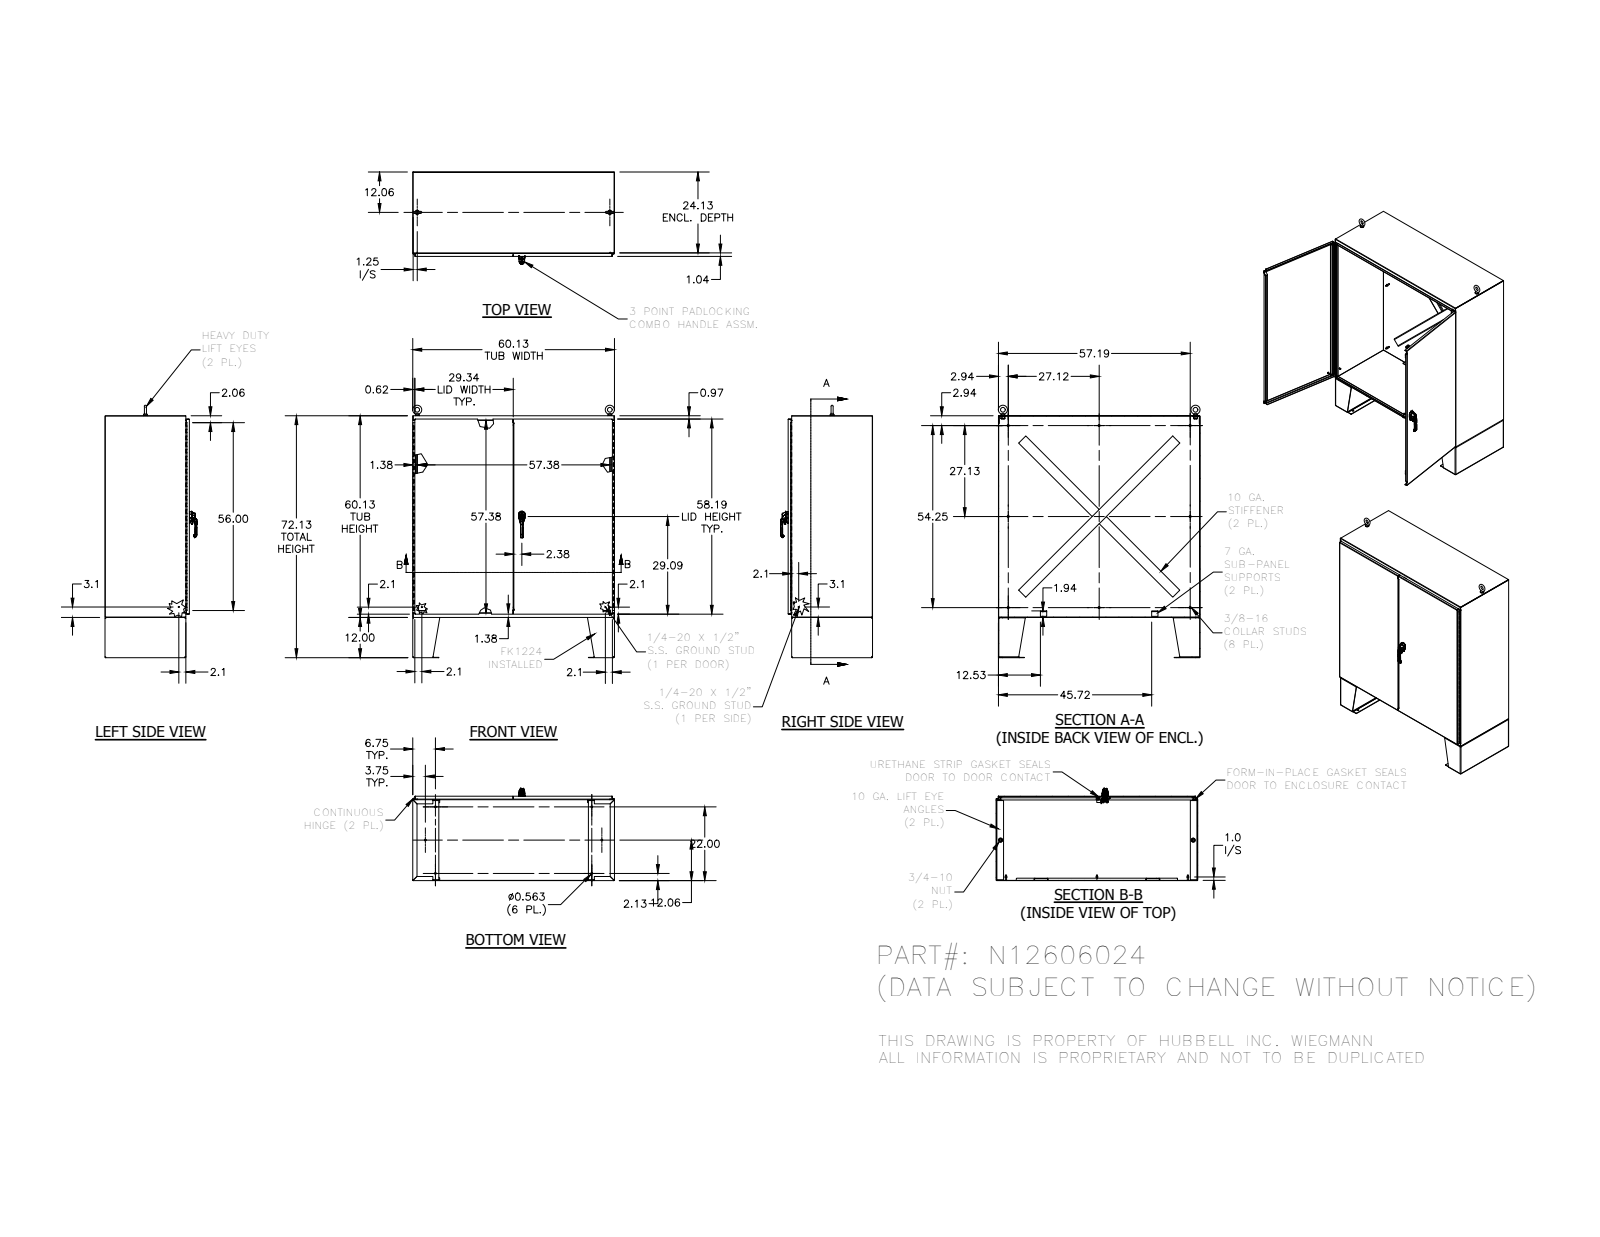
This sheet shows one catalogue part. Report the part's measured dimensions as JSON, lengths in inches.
{"part_name": "N12606024", "step_written_by": "SolidWorks 2018 (AUTOMOTIVE_DESIGN)", "units": "inches", "bodies": {"solids": 76, "faces": 2392, "planar": 1384, "cylindrical": 708, "other": 300}, "overall_size": [75.248, 60.125, 27.338], "volume_in3": 1653, "surface_area_in2": 33196, "round_holes": [[0.563, 18], [0.277, 8], [0.2, 4], [0.28, 3], [0.125, 2], [0.241, 2], [0.25, 2], [0.252, 2], [0.4, 2], [0.45, 2], [0.642, 2], [0.813, 2]], "round_bosses_or_shafts": [[0.33, 8], [0.625, 7], [0.25, 5], [0.337, 3], [1.25, 2], [1.12, 2], [1, 2], [0.75, 2]], "partial_cylinders_radius": [[0.031, 24], [0.094, 23], [0.219, 22], [0.05, 18], [0.025, 16], [0.125, 15], [0.03, 13], [0.067, 8]], "face_to_face_distances": [0.094, 25.067, 60.031, 24.973, 25.16, 60.125, 59.938, 0.125, 0.031, 0.125], "hole_center_spacings": [2.041, 5, 11.313, 20.659, 22.75, 23.293, 46.398, 50.669]}
